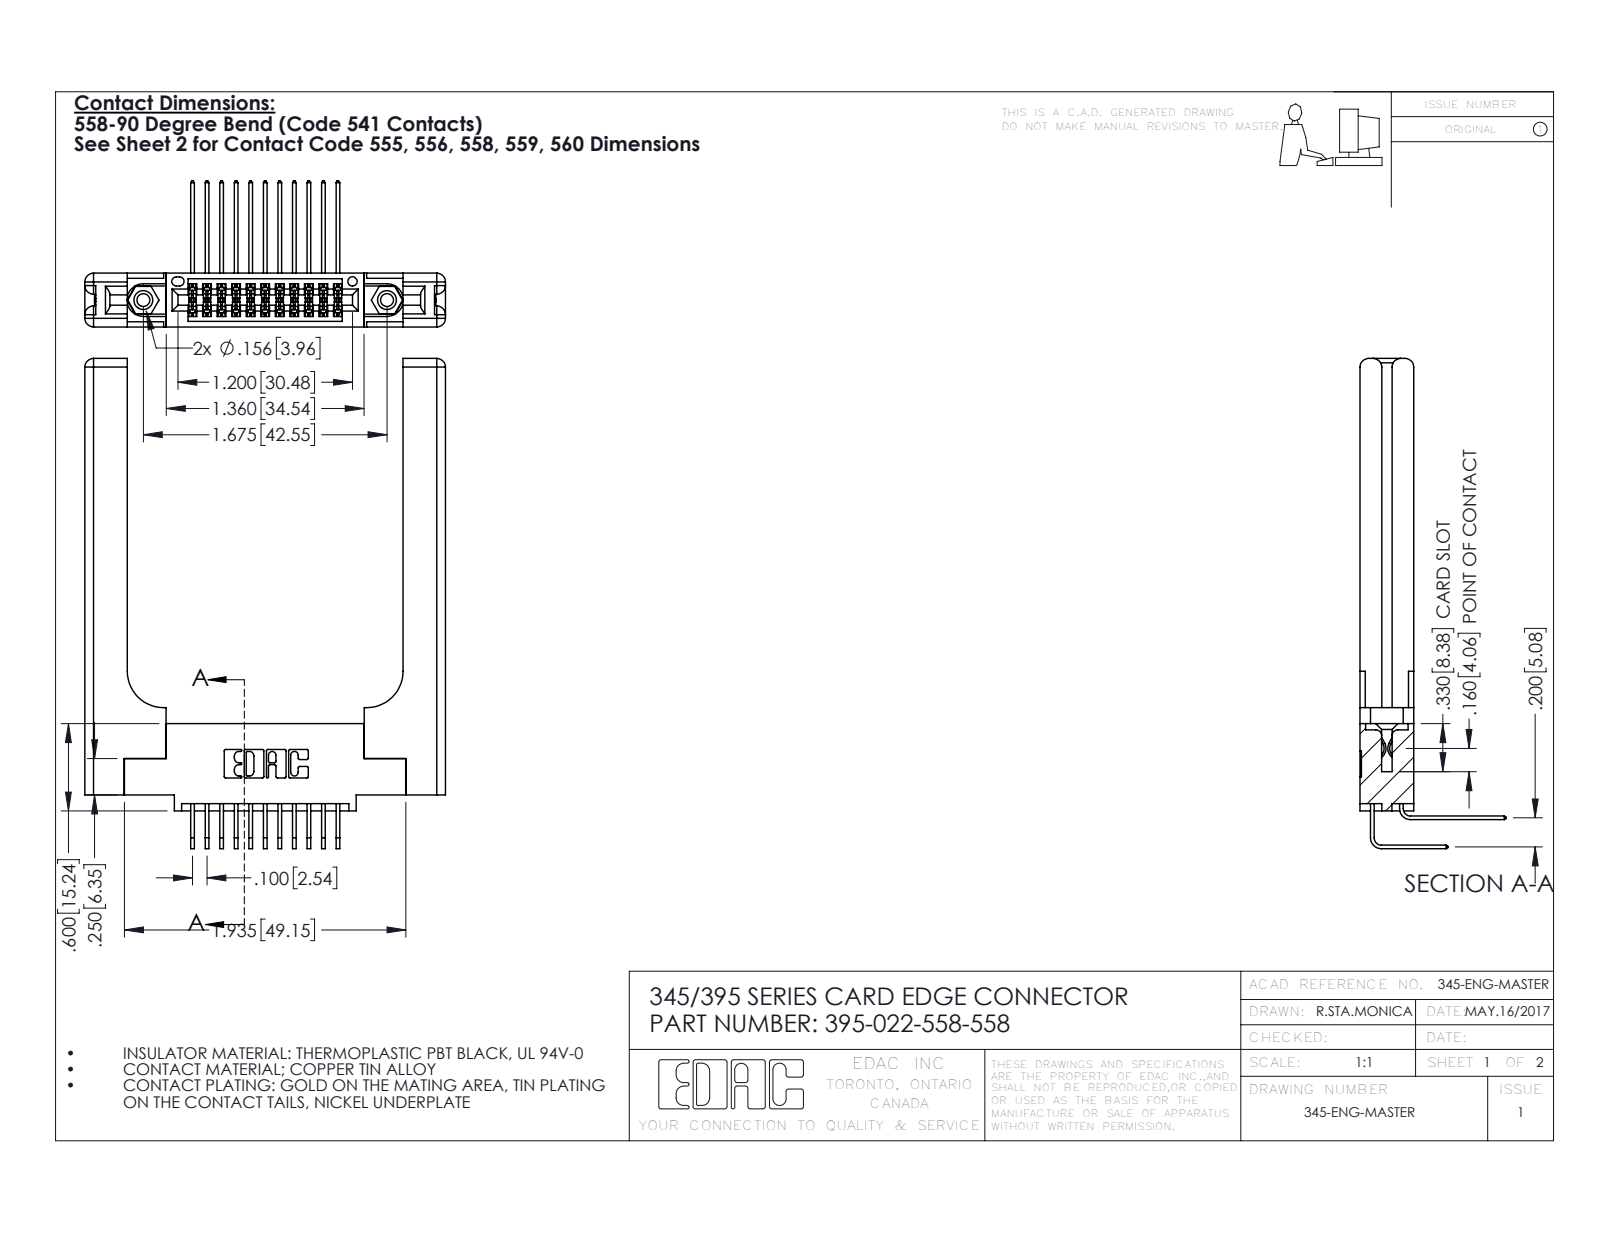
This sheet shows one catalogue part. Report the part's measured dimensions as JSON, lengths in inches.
{"part_name": "395-022-558-558; 345-220-058_345-220-058; 345-292-001_558 Tail - 2; 345-292-001_558 559 Tail - 1 (+2 more)", "step_written_by": "SolidWorks 2016 (CONFIG_CONTROL_DESIGN)", "units": "inches", "bodies": {"solids": 27, "faces": 1530, "planar": 1002, "cylindrical": 468, "other": 60}, "overall_size": [3.369, 2.479, 1.005], "volume_in3": 0.876, "surface_area_in2": 21.46, "round_holes": [[0.089, 2], [0.125, 2], [0.156, 2], [0.064, 1]], "round_bosses_or_shafts": [[0.155, 2]], "partial_cylinders_radius": [[0.006, 34], [0.01, 22], [0.06, 16], [0.007, 6], [0.031, 6], [0.026, 3], [0.014, 2], [0.019, 2]], "face_to_face_distances": [0.37, 0.072, 0.148, 0.15, 0.077, 0.298, 0.22, 0.2, 0.225, 1.896], "hole_center_spacings": [0.27, 1.443, 1.675]}
